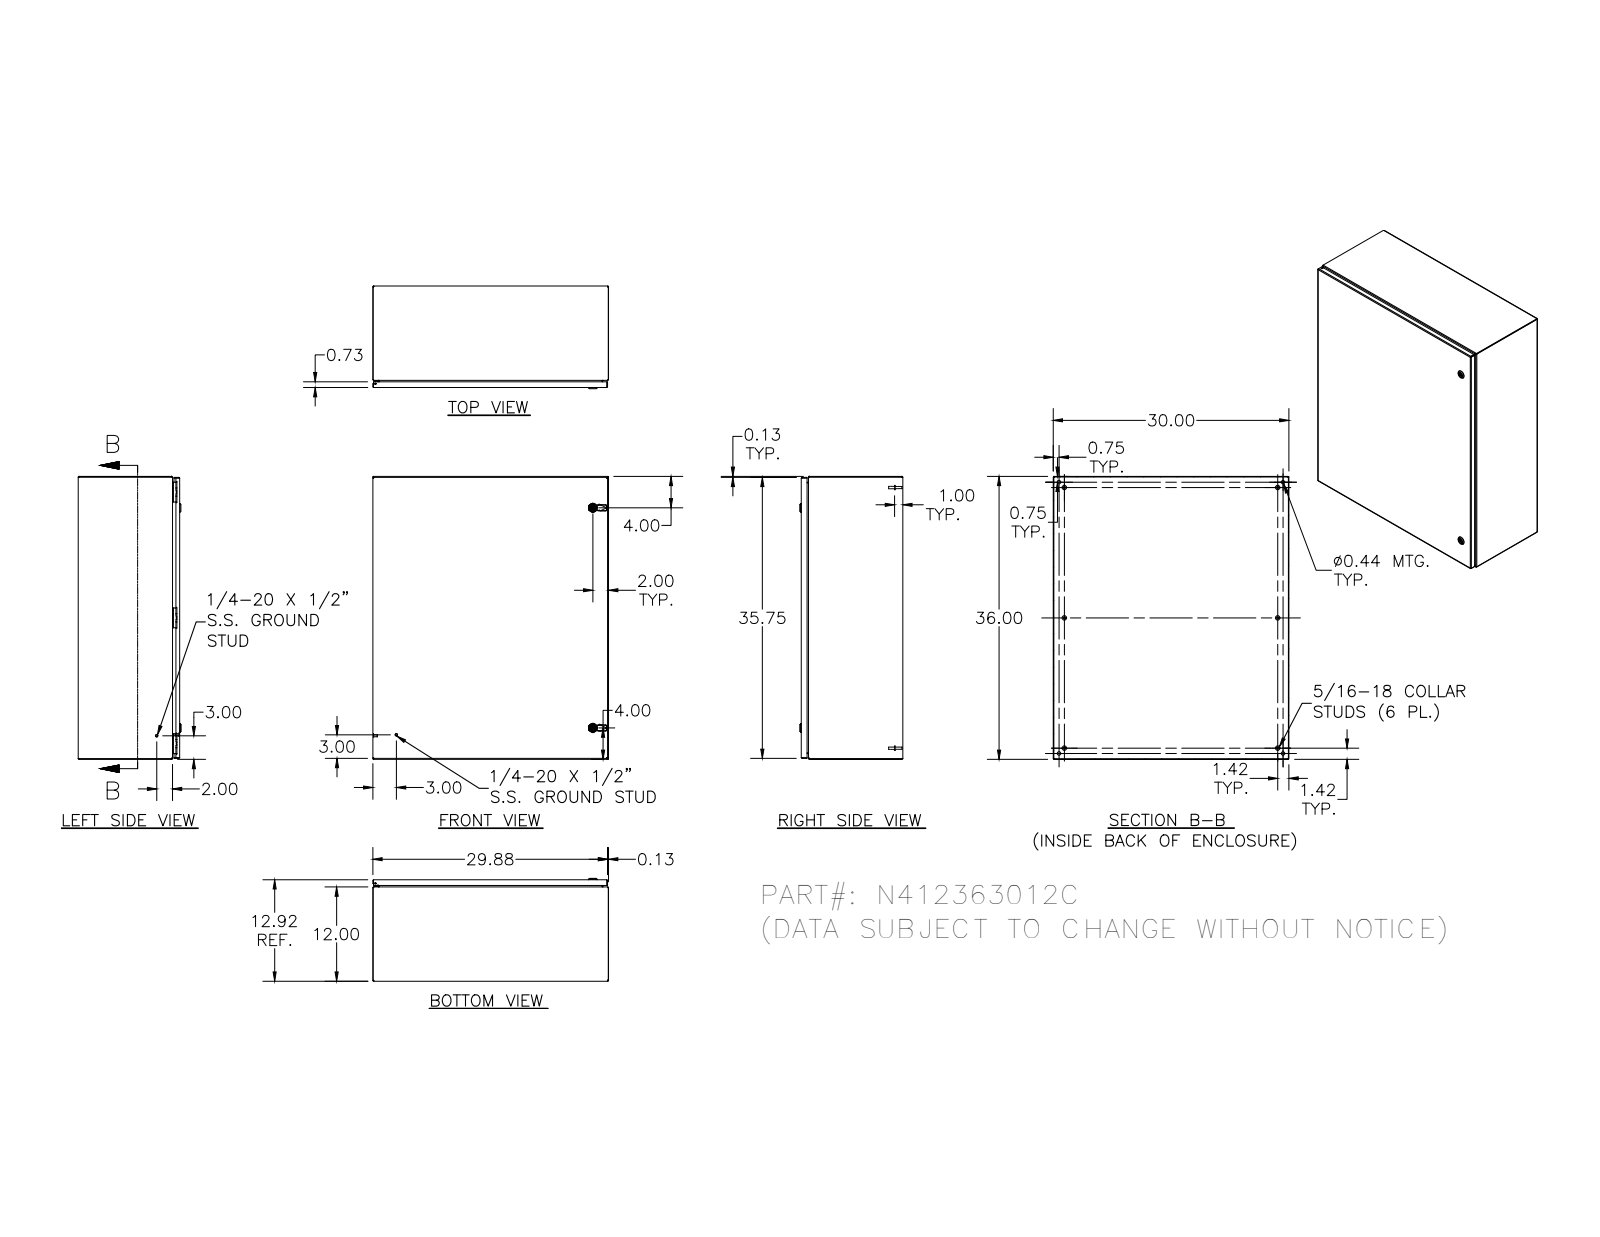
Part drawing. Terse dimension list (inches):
name: N412363012C; N4123630CLID; 35124; 1000-u155_asm (+8 more)
written by: Autodesk Inventor 2011 (AUTOMOTIVE_DESIGN)
unit: in
bodies: 49 solids, 2252 faces (831 planar, 856 cylindrical, 565 other)
size: 36 × 30 × 13.075
volume: 296.8 in³; area: 8 067 in²
holes: 7× ⌀0.188, 6× ⌀0.093, 6× ⌀0.152, 6× ⌀0.167, 6× ⌀0.172, 4× ⌀0.437, 3× ⌀0.156, 2× ⌀0.197, 2× ⌀0.315, 2× ⌀0.394, 2× ⌀0.402, 2× ⌀0.634
bosses: 14× ⌀0.25, 6× ⌀0.563, 6× ⌀0.36, 6× ⌀0.32, 6× ⌀0.3, 6× ⌀0.275, 6× ⌀0.256, 6× ⌀0.164
rounds: 54× R0.012, 38× R0.05, 34× R0.031, 26× R0.016, 24× R0.125, 23× R0.02, 20× R0.105, 12× R0.032
face distances: 0.074, 12.843, 0.074, 12.769, 12.917, 35.926, 29.926, 29.852, 29.926, 30
hole spacings: 16, 32, 0.66, 0.656, 1.307, 1.965, 16.008, 0.5
